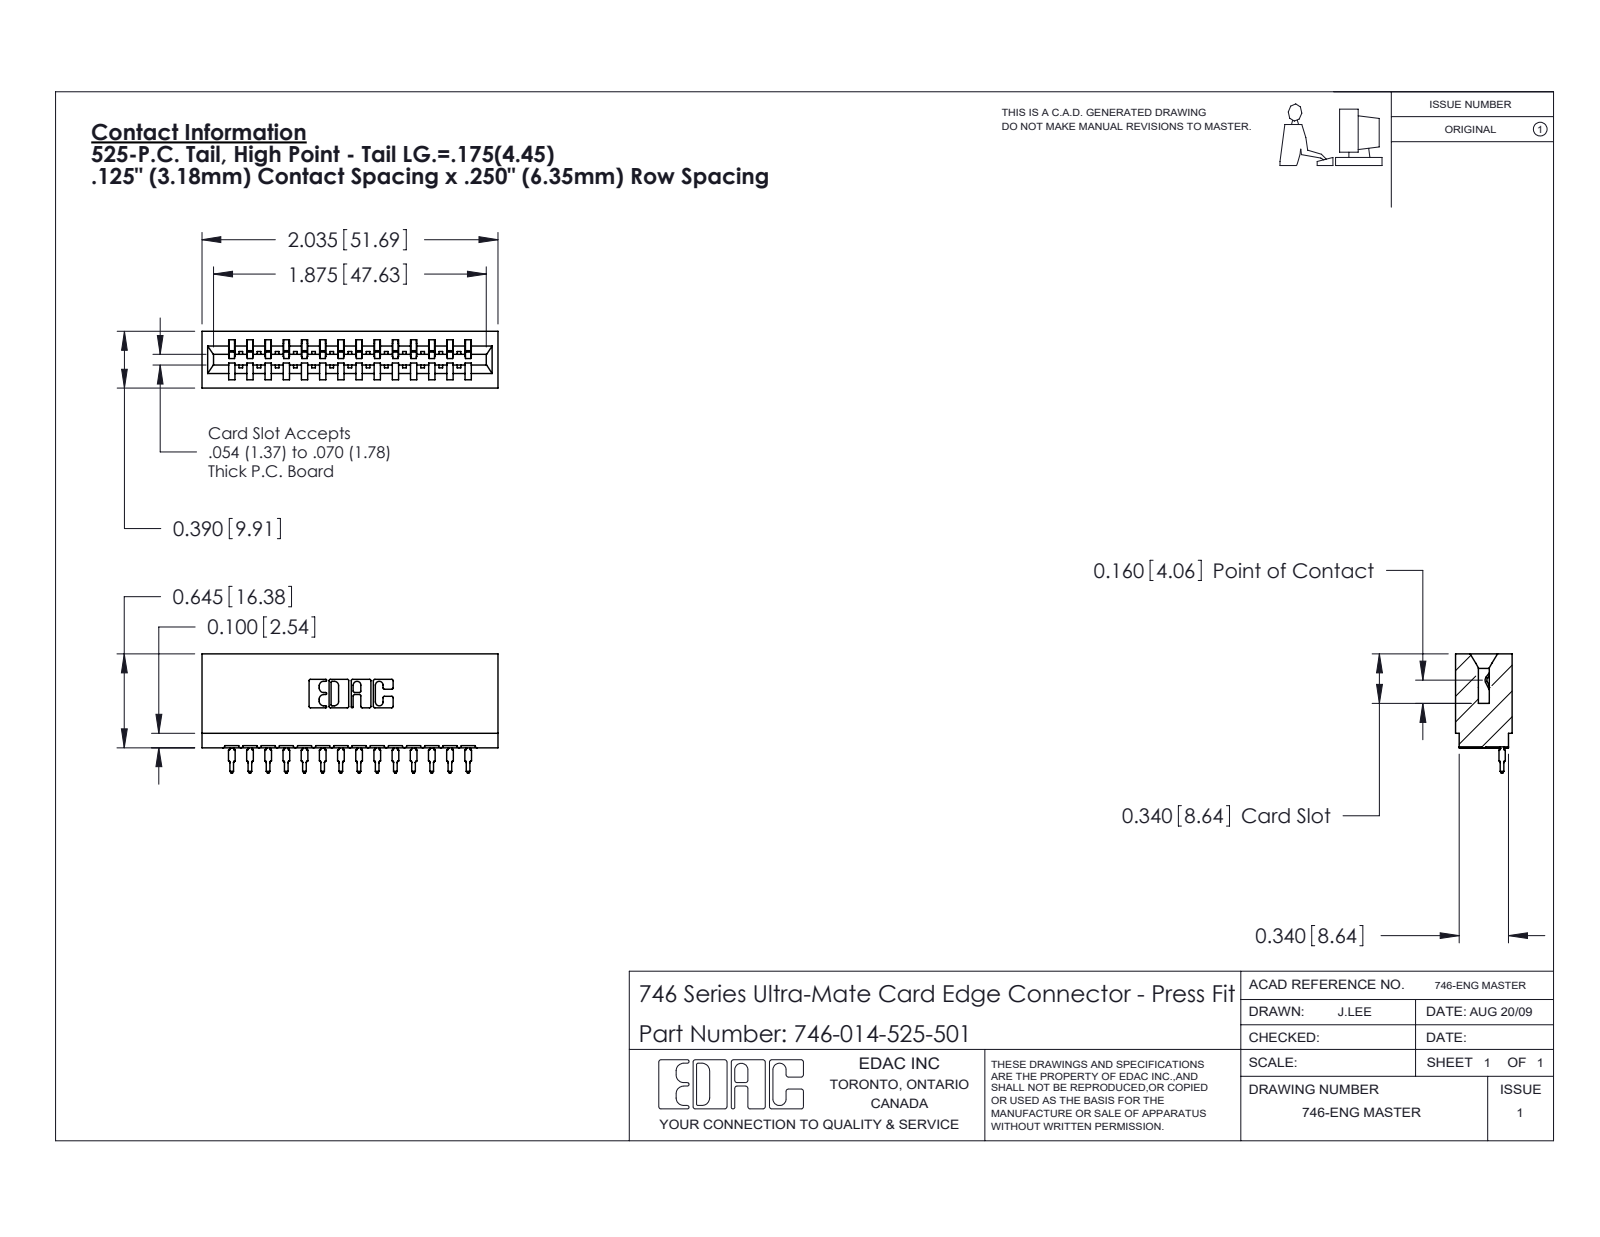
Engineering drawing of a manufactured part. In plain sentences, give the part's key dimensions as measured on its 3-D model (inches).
The part is named "746-292-001_525; 746 Part_.340 Slot Depth - 01; 746-014-525-501". Its 3-D file was written by "SolidWorks 2020 (CONFIG_CONTROL_DESIGN)". It is 15 solids with 1609 faces: 937 planar, 308 cylindrical and 364 other. Overall it measures 2.035 by 0.819 by 0.39 inches. Its volume is 0.364 cubic inches and its surface area 11.68 square inches. Partial cylindrical surfaces (rounded edges, fillets, slot ends): 28 of radius 0.021, 22 of radius 0.01, 15 of radius 0.015, 6 of radius 0.007, 6 of radius 0.031, 4 of radius 0.005, 4 of radius 0.011, 3 of radius 0.026. The main face-to-face distances are 0.25, 0.333, 0.5, 0.057, 0.39, 0.125, 0.292, 0.125, 0.042, 0.542.
